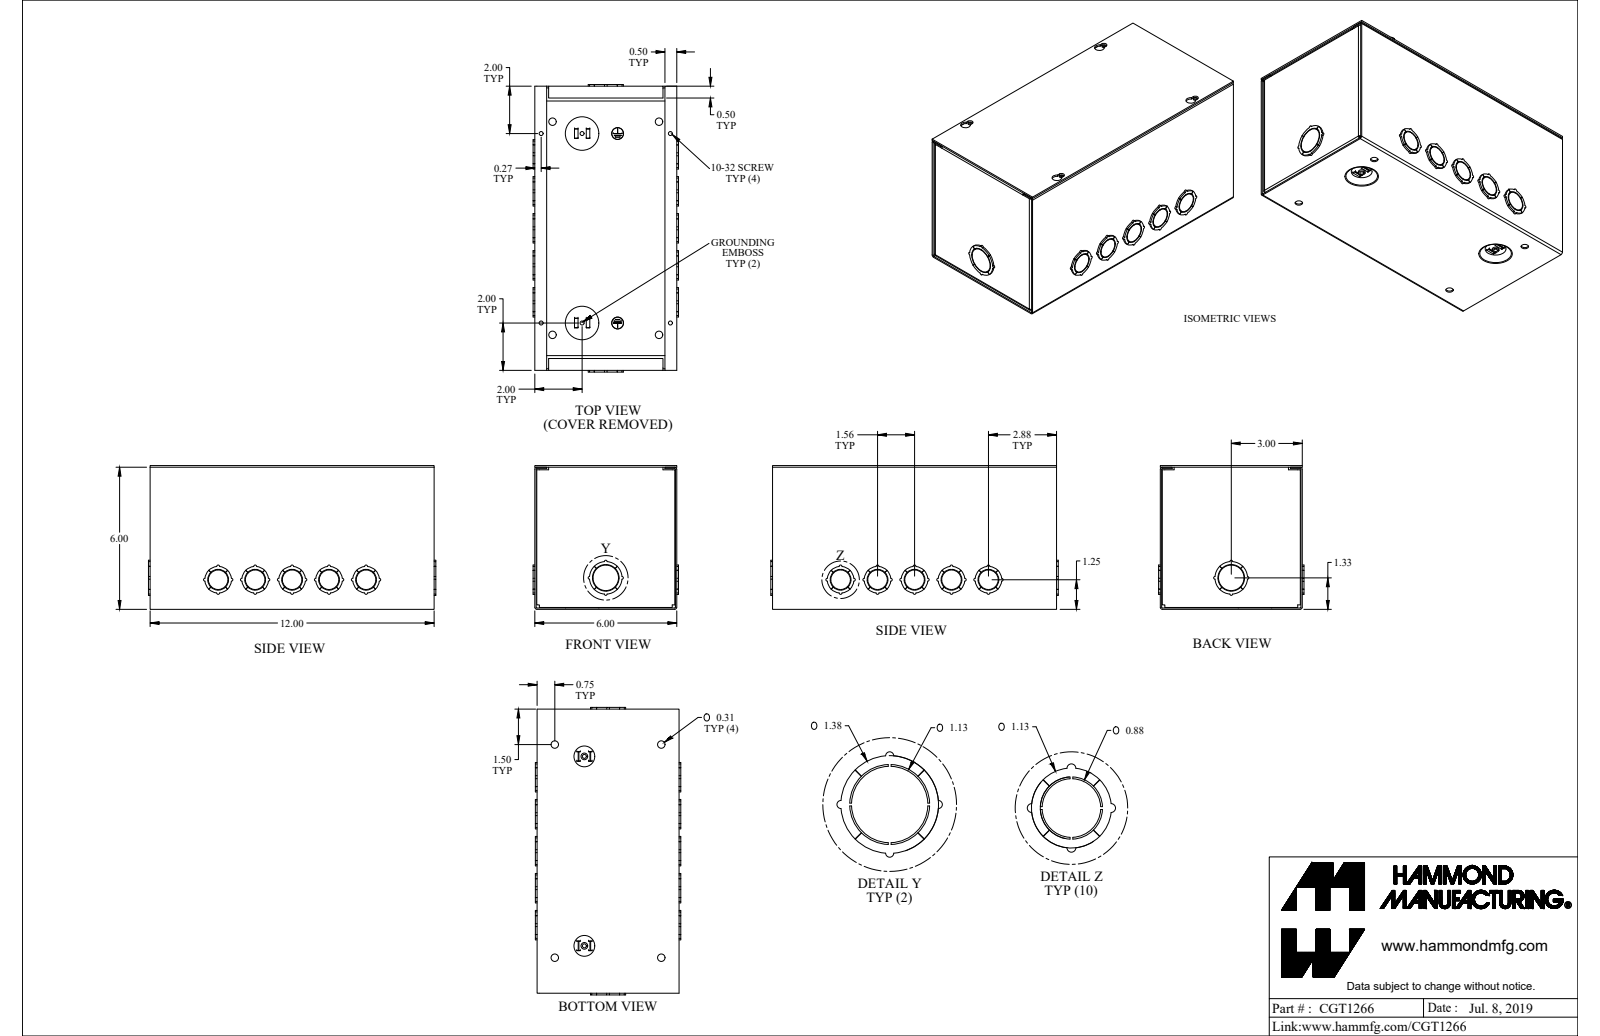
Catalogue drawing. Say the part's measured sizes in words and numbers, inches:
The part is named "CGT1266". Its 3-D file was written by "SolidWorks 2021 (AUTOMOTIVE_DESIGN)". It is 6 solids with 778 faces: 408 planar, 356 cylindrical and 14 other. Overall it measures 12.144 by 6.247 by 6.144 inches. Its volume is 25.11 cubic inches and its surface area 793 square inches. Round holes: 6 of diameter 0.17, 5 of diameter 0.875, 4 of diameter 0.312, 2 of diameter 0.5, 1 of diameter 1.125. Round bosses or shafts: 5 of diameter 1.125, 5 of diameter 0.825, 2 of diameter 0.492, 2 of diameter 0.375, 2 of diameter 0.284, 2 of diameter 0.19, 1 of diameter 1.375, 1 of diameter 1.075. Partial cylindrical surfaces (rounded edges, fillets, slot ends): 20 of radius 0.062, 8 of radius 0.036, 8 of radius 0.057, 8 of radius 0.108, 4 of radius 0.029, 4 of radius 0.057, 4 of radius 0.086, 4 of radius 0.125. The main face-to-face distances are 0.057, 5.943, 0.072, 6, 5.886, 6.015, 6.072, 11.928, 12, 11.856. The hole center spacings are 0.693, 5.005, 8, 8.513, 9.851, 1.346, 1.5, 1.562.
